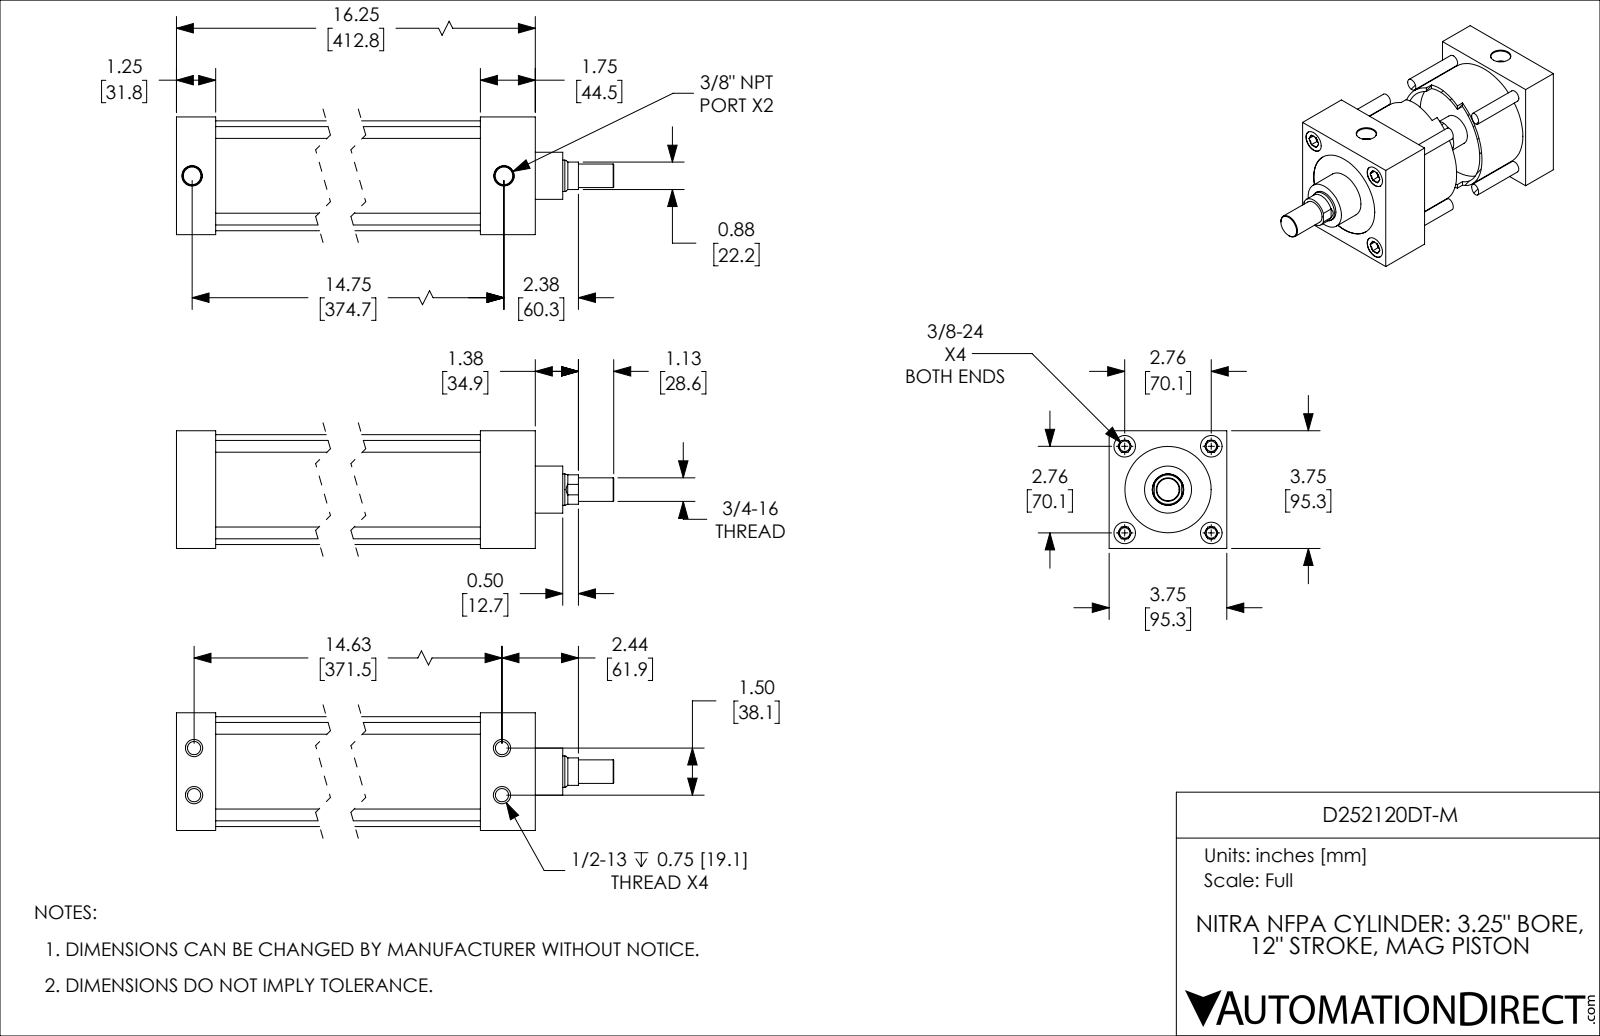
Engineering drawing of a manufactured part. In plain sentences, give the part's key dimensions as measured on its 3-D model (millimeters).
The part is named "D252120DT-M; D252120DT-M_BODY; D252120DT-M_PISTON_KK1". Its 3-D file was written by "SolidWorks 2019 (CONFIG_CONTROL_DESIGN)". It is 2 solids with 198 faces: 58 planar, 62 cylindrical and 78 other. Overall it measures 476.3 by 95.3 by 95.3 millimeters. Its volume is 1 402 000 cubic millimeters and its surface area 354 900 square millimeters. Round holes: 4 of diameter 8.4, 4 of diameter 10.7, 4 of diameter 17.4, 2 of diameter 14.3, 1 of diameter 25.4, 1 of diameter 69.9, 1 of diameter 82.6. Round bosses or shafts: 4 of diameter 9.5, 1 of diameter 88.9, 1 of diameter 82.5, 1 of diameter 38.1, 1 of diameter 25.4, 1 of diameter 19.1. Partial cylindrical surfaces (rounded edges, fillets, slot ends): 1 of radius 11.9. The main face-to-face distances are 31.8, 95.3, 368.3, 336.6, 63.5, 304.8, 412.8, 381, 349.3, 44.5. The hole center spacings are 19.1, 49.6, 70.1, 373.6, 38.1, 99.1, 371.5, 373.4.
